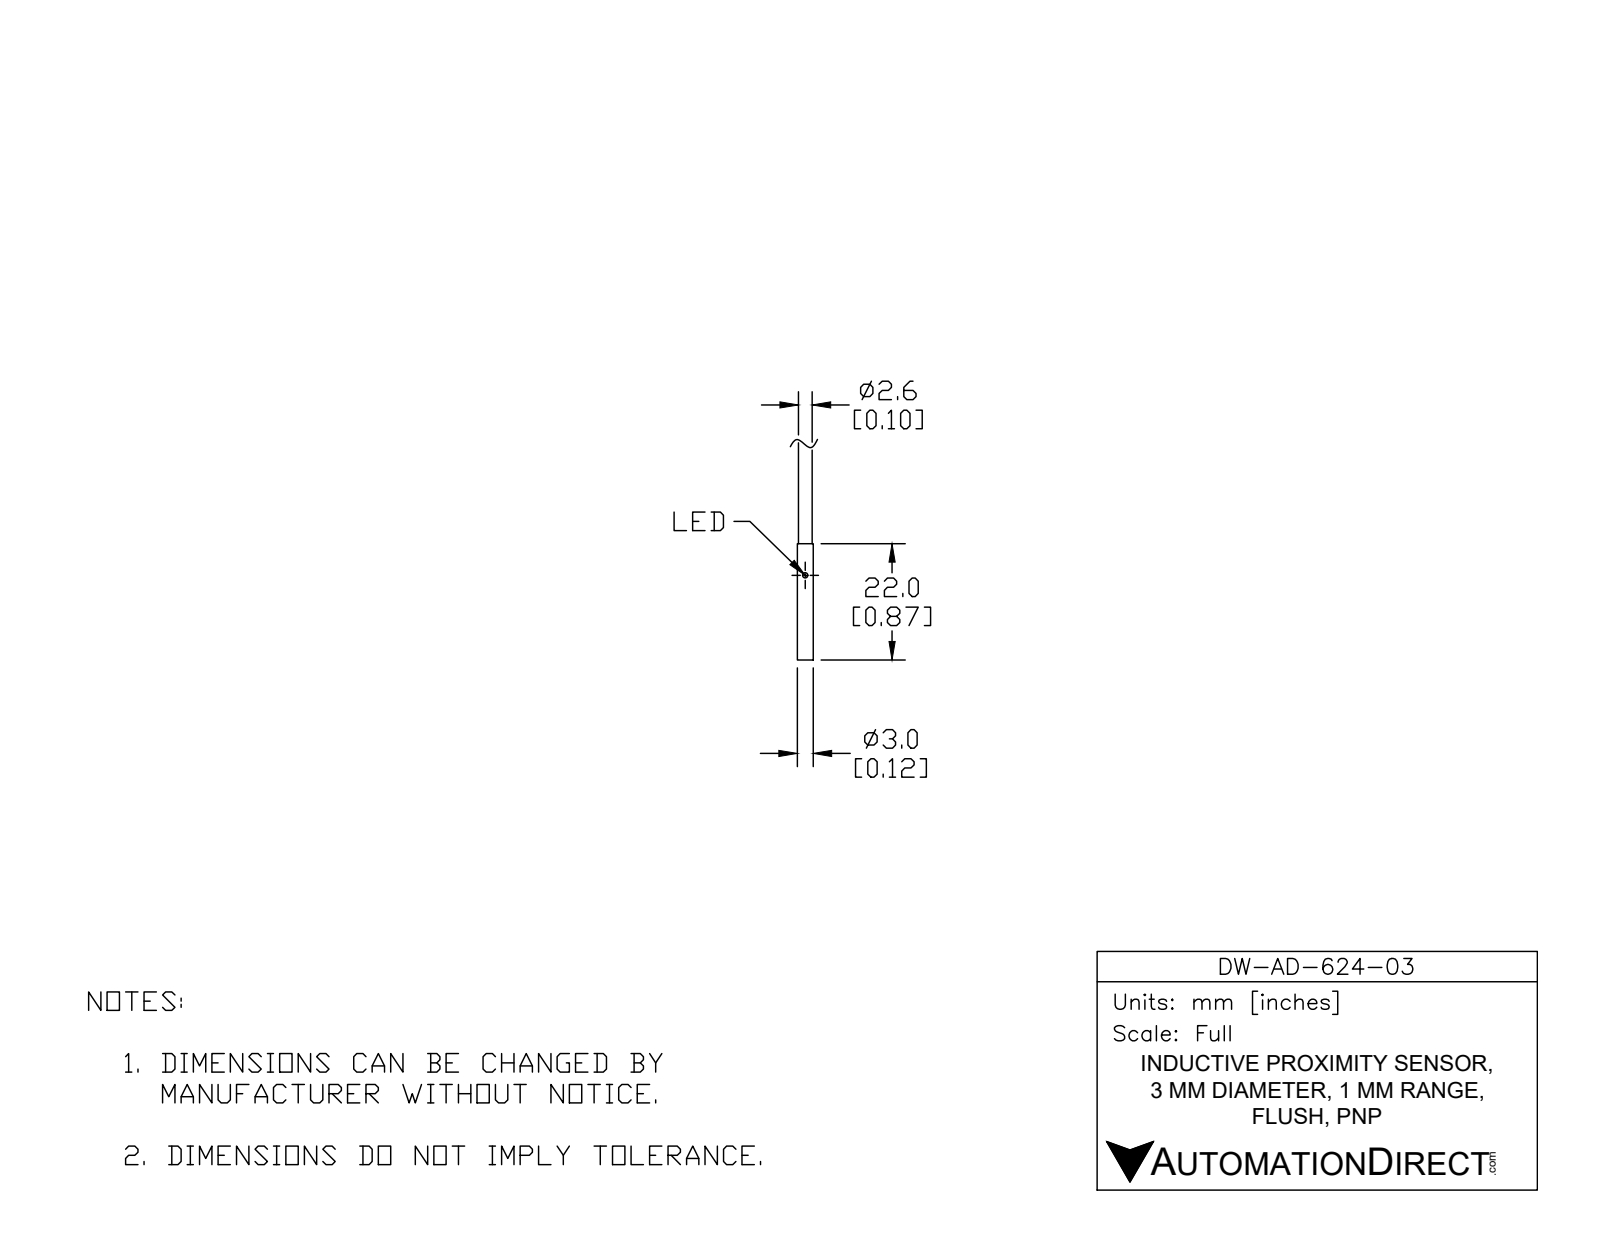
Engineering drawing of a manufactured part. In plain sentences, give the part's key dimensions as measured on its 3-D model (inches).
The part is named "DW-AD-624-03". Its 3-D file was written by "SolidWorks 2017 (AUTOMOTIVE_DESIGN)". It is 3 solids with 13 faces: 5 planar, 5 cylindrical and 3 other. Overall it measures 1.418 by 0.118 by 0.118 inches. Its volume is 0.008 cubic inches and its surface area 0.895 square inches. Round holes: 1 of diameter 0.039, 1 of diameter 0.106. Round bosses or shafts: 1 of diameter 0.118, 1 of diameter 0.102. The main face-to-face distances are 0.03, 0.669, 0.639, 0.866, 0.836, 0.197.
